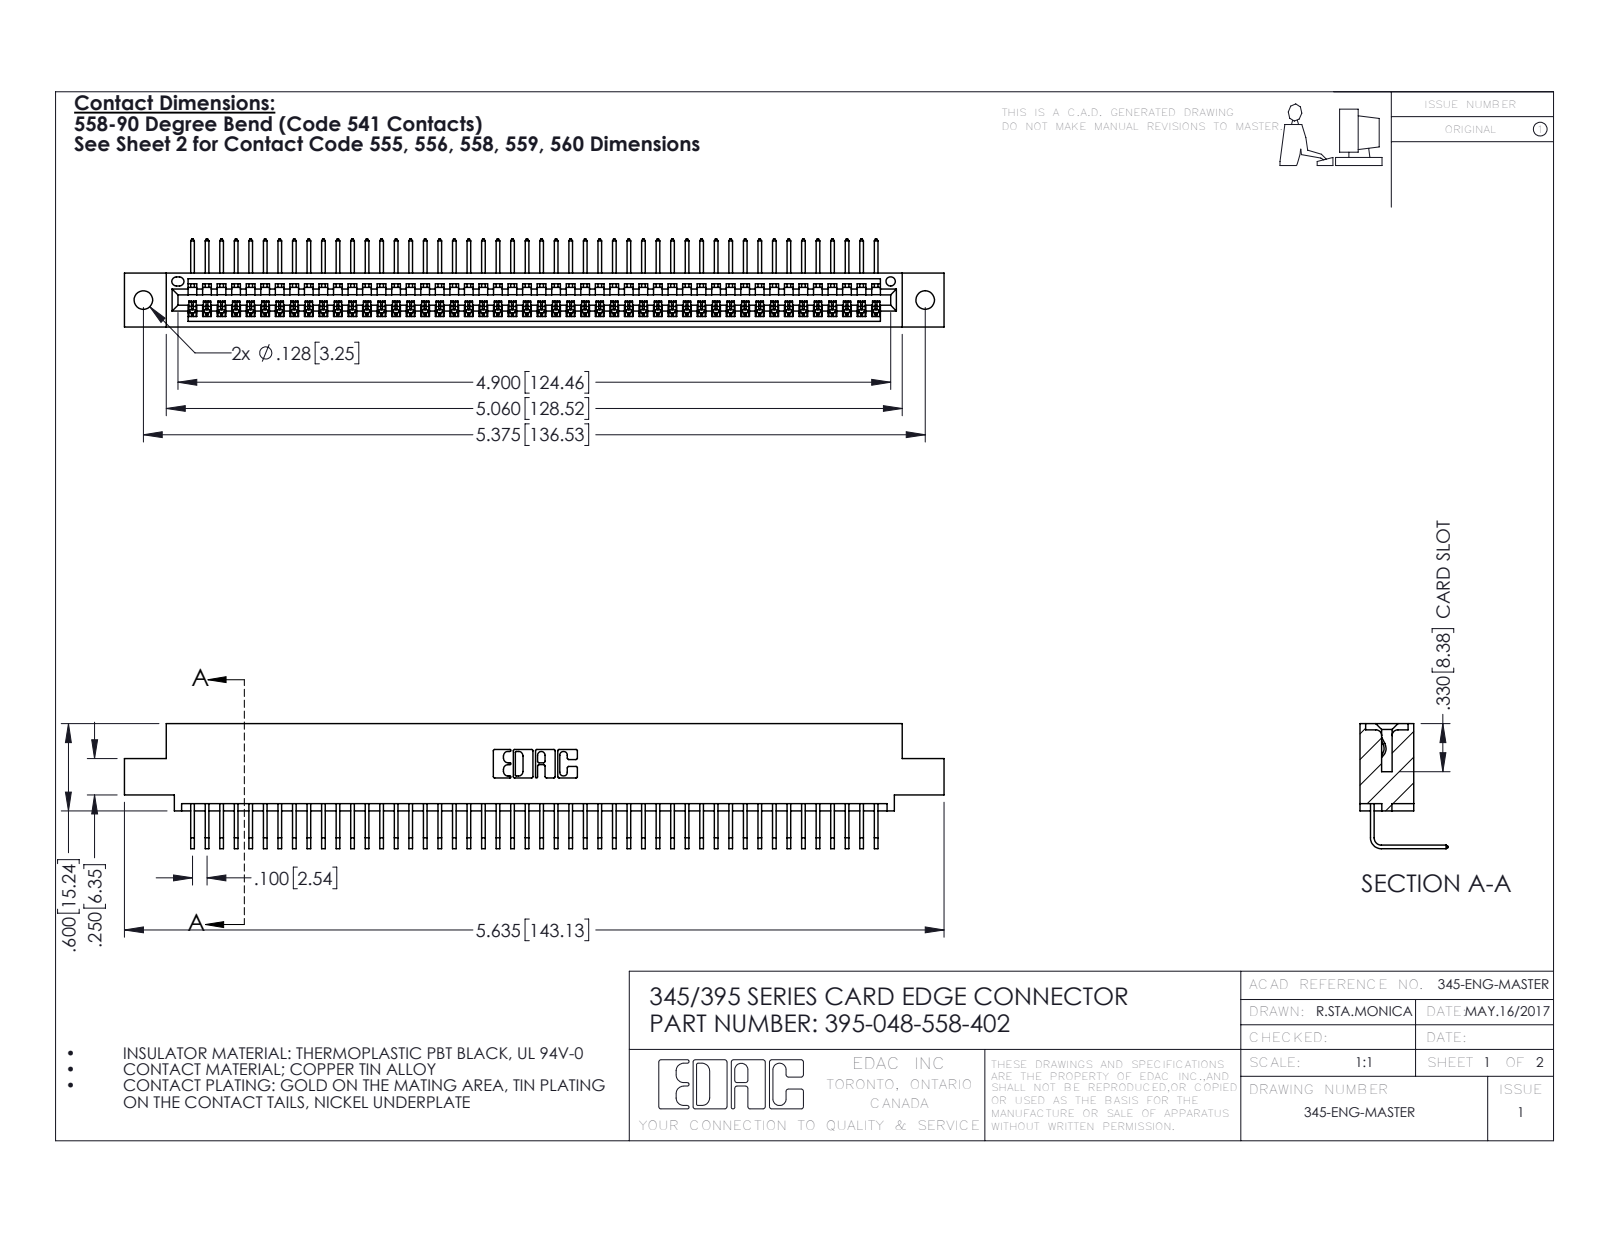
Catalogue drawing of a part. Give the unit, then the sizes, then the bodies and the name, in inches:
Units: inches
Overall size (bounding box): 5.635 × 0.859 × 0.605
Round holes (diameter × count): ⌀0.128 ×2, ⌀0.064 ×1
Partial cylindrical surfaces — rounded edges, fillets, slot ends (radius × count): R0.006 ×96, R0.01 ×22, R0.007 ×6, R0.031 ×6, R0.026 ×3, R0.031 ×2, R0.04 ×2, R0.014 ×1
Main face-to-face distances: 0.072, 0.298, 0.37, 0.2, 0.098, 0.272, 0.025, 0.225, 0.149, 0.072
Hole centre spacings: 0.27, 5.139, 5.375
Volume: 0.836 in³ · Surface area: 29.5 in²
Bodies: 49 solids, 3010 faces (2100 planar, 910 cylindrical, 0 other)
Part name (STEP PRODUCT): 345-292-001_558 Tail - 2; 345 Part_0.110 Offset - 0.128 Dia; 395-048-558-402
STEP written by: SolidWorks 2016 (CONFIG_CONTROL_DESIGN)
